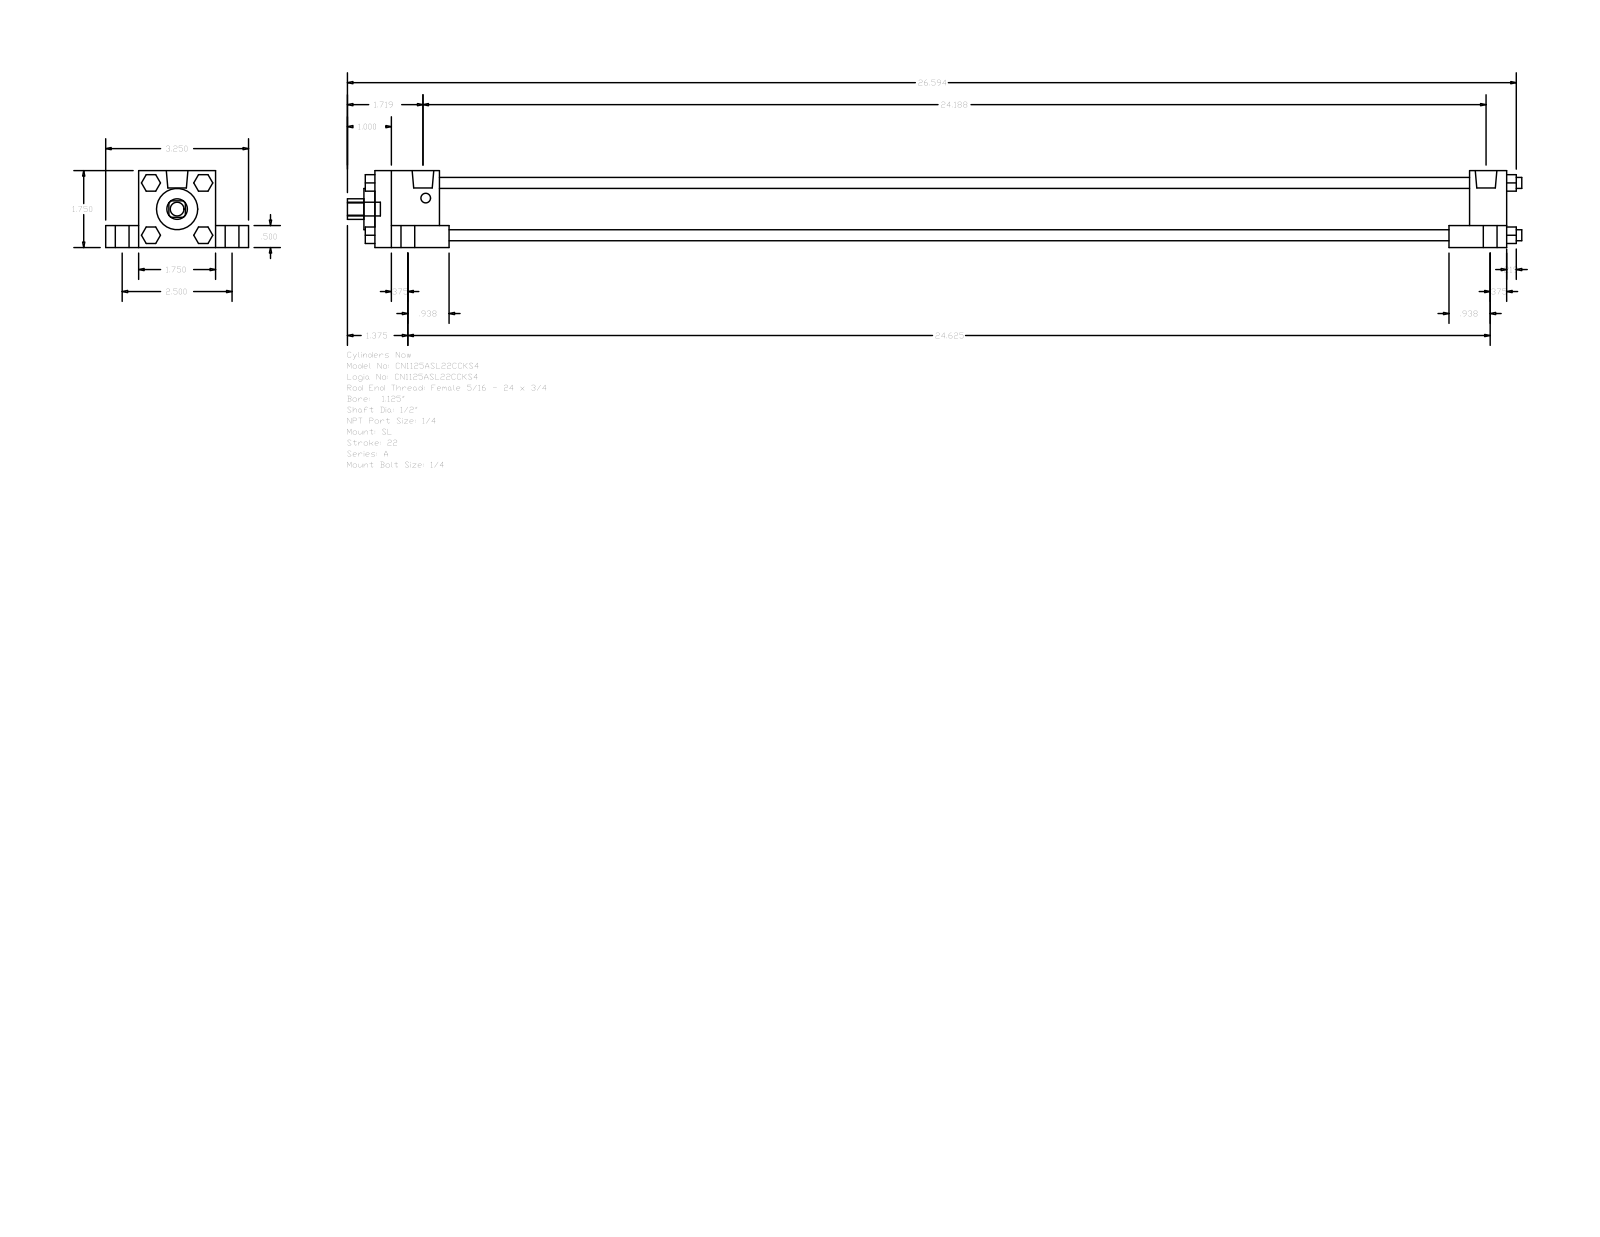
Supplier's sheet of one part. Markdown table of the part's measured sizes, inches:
| quantity | value |
| --- | --- |
| part name | A_SL__0112_0.5 |
| STEP written by | GSSL Pune (CONFIG_CONTROL_DESIGN) |
| units | inches |
| bodies | 0 solids, 150 faces (114 planar, 36 cylindrical, 0 other) |
| overall size | 26.719 × 3.25 × 1.75 |
| round holes (diameter × count) | 0.5 × 1, 0.937 × 1, 1.255 × 1 |
| round bosses / shafts (diameter × count) | 0.313 × 5, 0.563 × 4, 0.25 × 4, 0.219 × 4, 0.492 × 2 |
| partial cylindrical surfaces (radius × count) | 0.234 × 1 |
| main face-to-face distances | 1.75, 1.25, 0.5, 0.75, 2.5, 24.281, 25.75, 24.906, 0.844, 1.469 |
